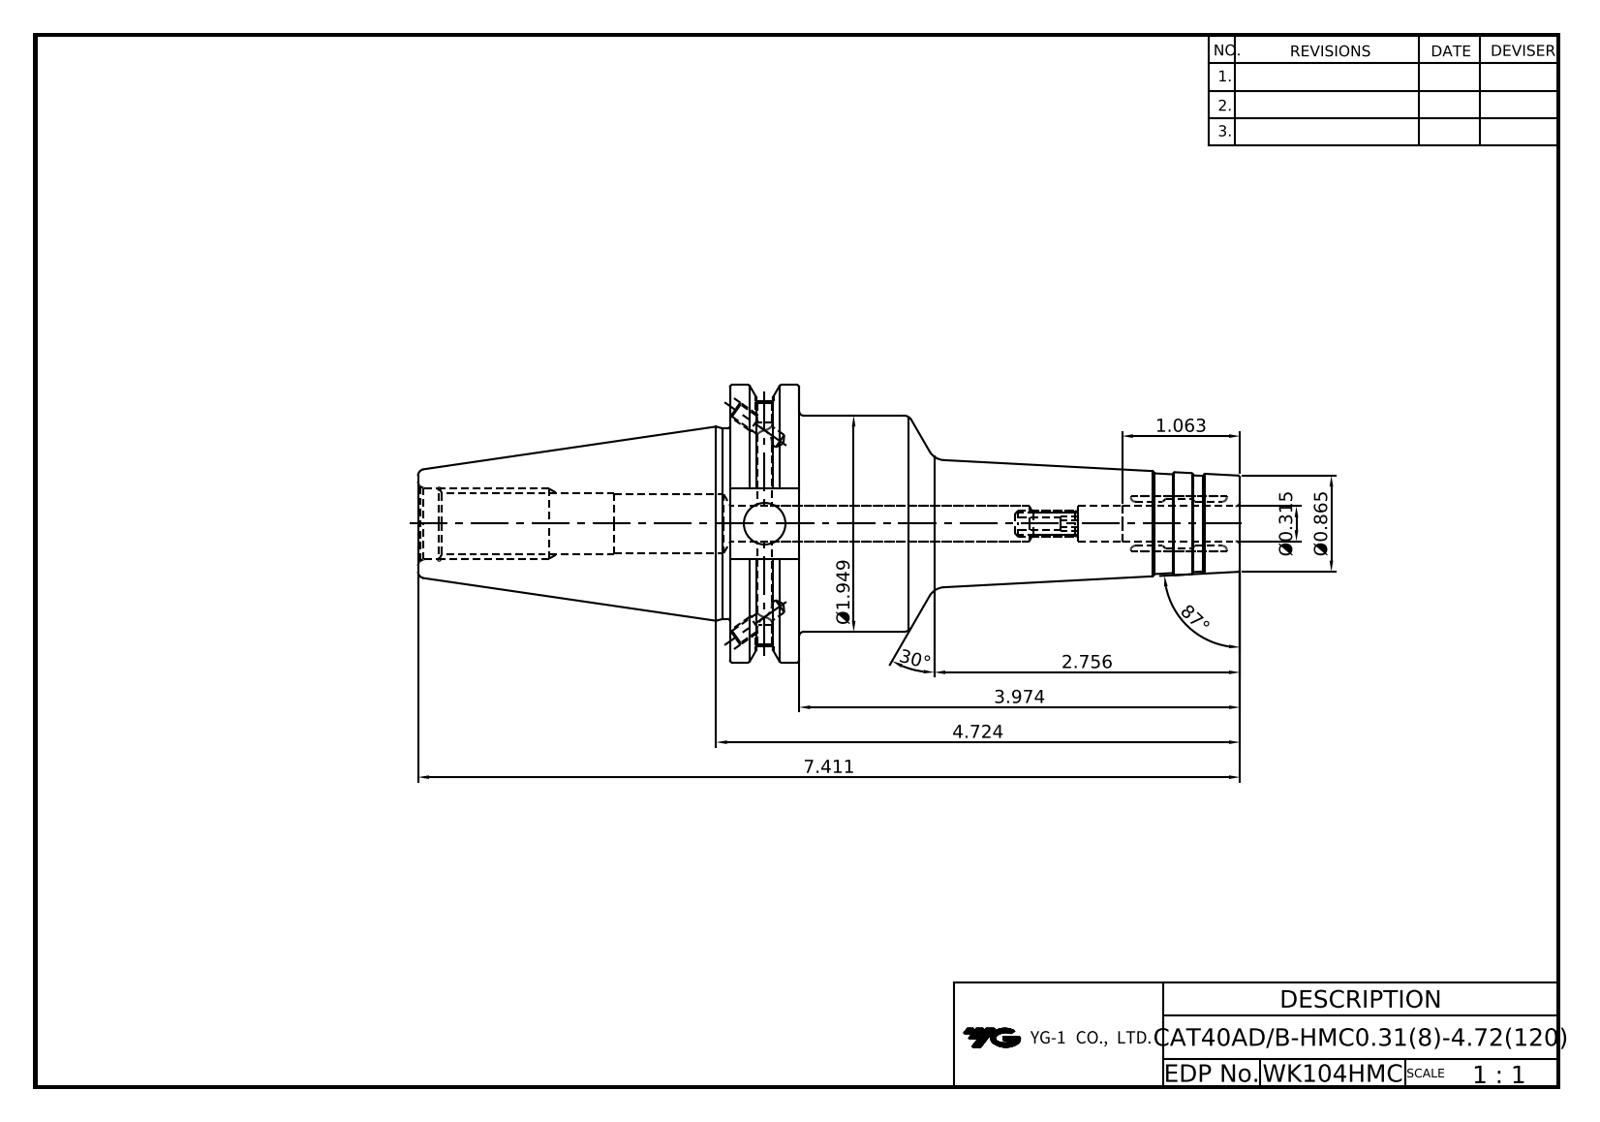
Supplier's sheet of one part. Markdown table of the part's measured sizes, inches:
| quantity | value |
| --- | --- |
| part name | LO-CAT40ADB-HMC8-120 |
| STEP written by | Autodesk Inventor 2020 (AUTOMOTIVE_DESIGN) |
| units | inches |
| bodies | 1 solid, 108 faces (36 planar, 31 cylindrical, 41 other) |
| overall size | 7.411 × 2.5 × 2.405 |
| volume | 11.53 in³ |
| surface area | 50.38 in² |
| round holes (diameter × count) | 0.128 × 4, 0.157 × 2, 0.165 × 2, 0.194 × 1, 0.315 × 1, 0.339 × 1, 0.375 × 1, 0.512 × 1, 0.527 × 1, 0.642 × 1 |
| round bosses / shafts (diameter × count) | 2.5 × 1, 1.949 × 1, 1.717 × 1 |
| partial cylindrical surfaces (radius × count) | 0.322 × 1, 1.108 × 1 |
| main face-to-face distances | 0.625, 4.6, 3.974, 1.874, 0.645, 2.812, 3.437, 7.411, 3.05, 0.238 |
